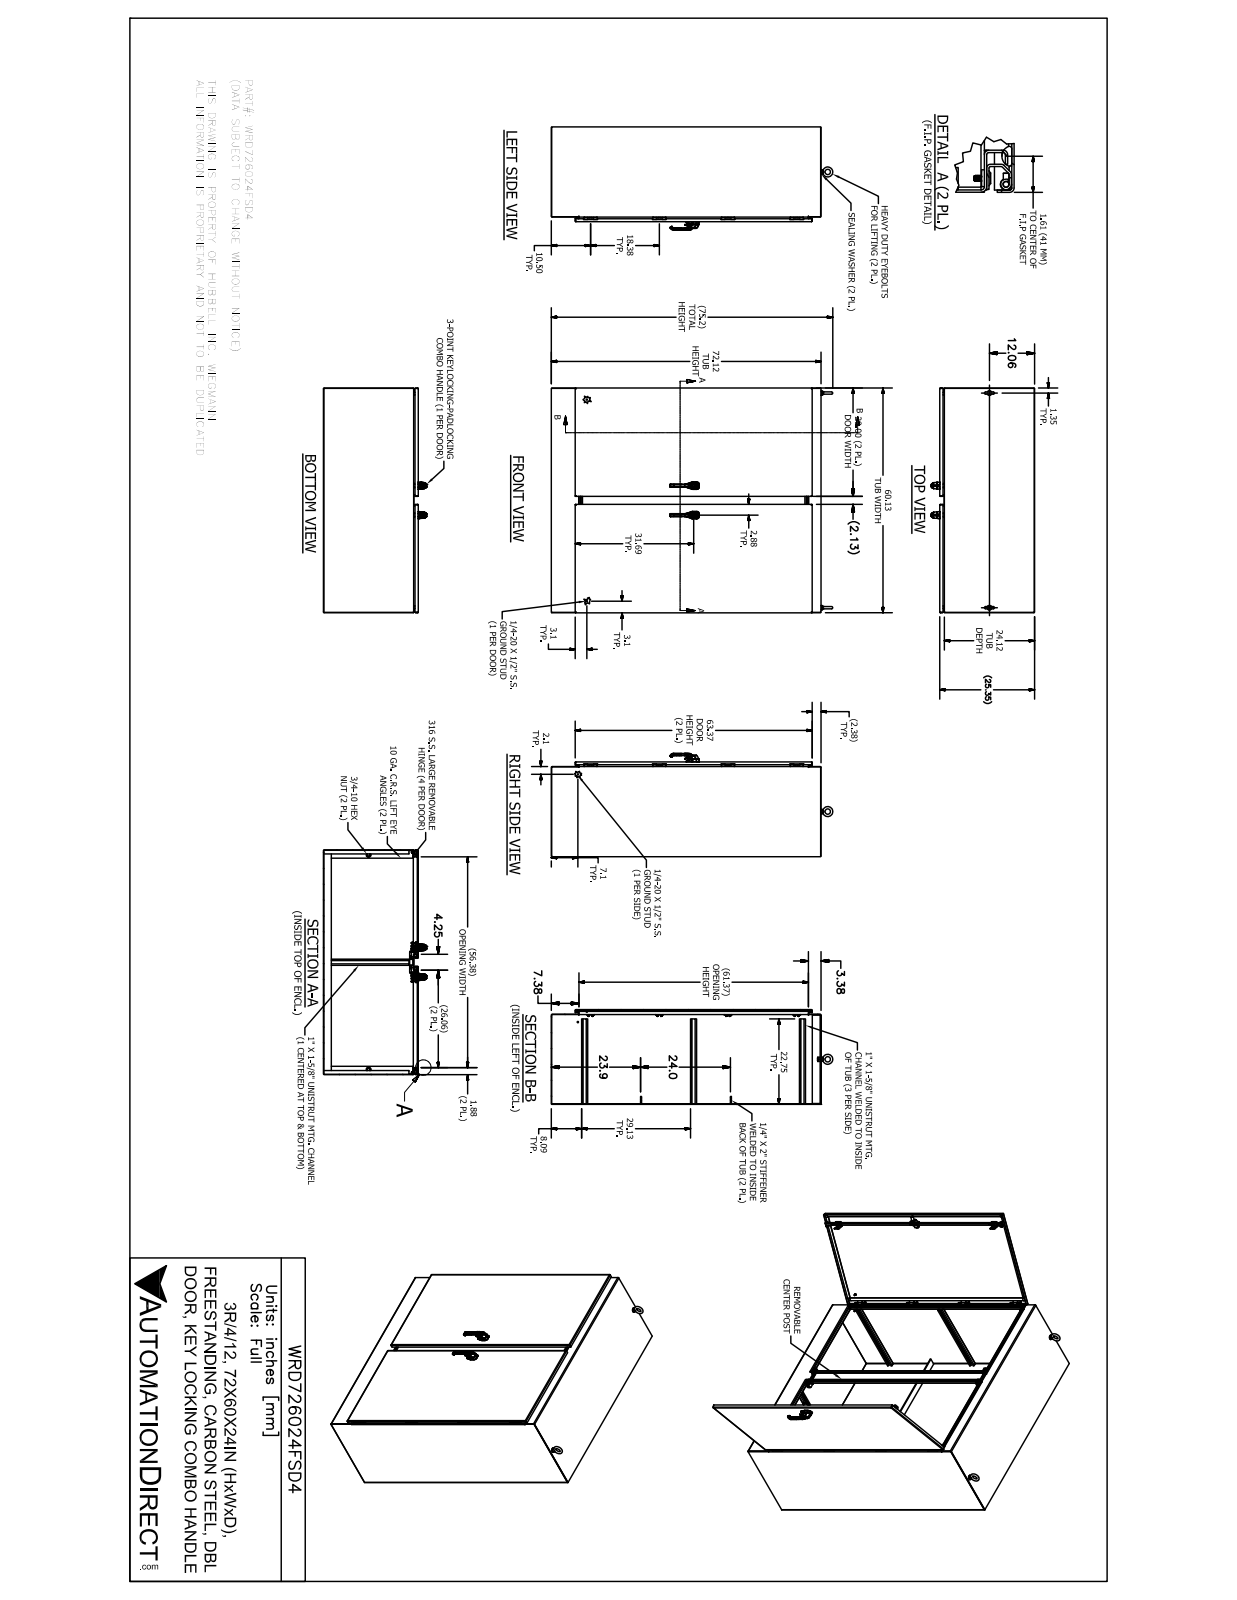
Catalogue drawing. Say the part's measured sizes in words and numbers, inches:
The part is named "WRD726024FSD4". Its 3-D file was written by "SolidWorks 2017 (AUTOMOTIVE_DESIGN)". It is 155 solids with 3276 faces: 1520 planar, 1096 cylindrical and 660 other. Overall it measures 75.248 by 60.133 by 27.527 inches. Its volume is 2 038 cubic inches and its surface area 37 109 square inches. Round holes: 20 of diameter 0.266, 16 of diameter 0.23, 16 of diameter 0.281, 16 of diameter 0.65, 8 of diameter 0.2, 8 of diameter 0.277, 6 of diameter 0.281, 4 of diameter 0.156, 4 of diameter 0.252, 4 of diameter 0.4, 4 of diameter 0.45, 3 of diameter 0.241. Round bosses or shafts: 15 of diameter 0.625, 13 of diameter 0.25, 4 of diameter 0.533, 4 of diameter 0.438, 4 of diameter 0.375, 4 of diameter 0.313, 4 of diameter 0.213, 3 of diameter 1. Partial cylindrical surfaces (rounded edges, fillets, slot ends): 47 of radius 0.062, 32 of radius 0.05, 32 of radius 0.125, 16 of radius 0.01, 16 of radius 0.019, 16 of radius 0.025, 16 of radius 0.053, 16 of radius 0.067. The main face-to-face distances are 0.104, 25.245, 25.141, 25.349, 60.021, 72.021, 24.021, 1.224, 59.917, 60.125. The hole center spacings are 1, 18.375, 36.75, 61.676, 61.676, 1.102, 17.375, 18.375.
